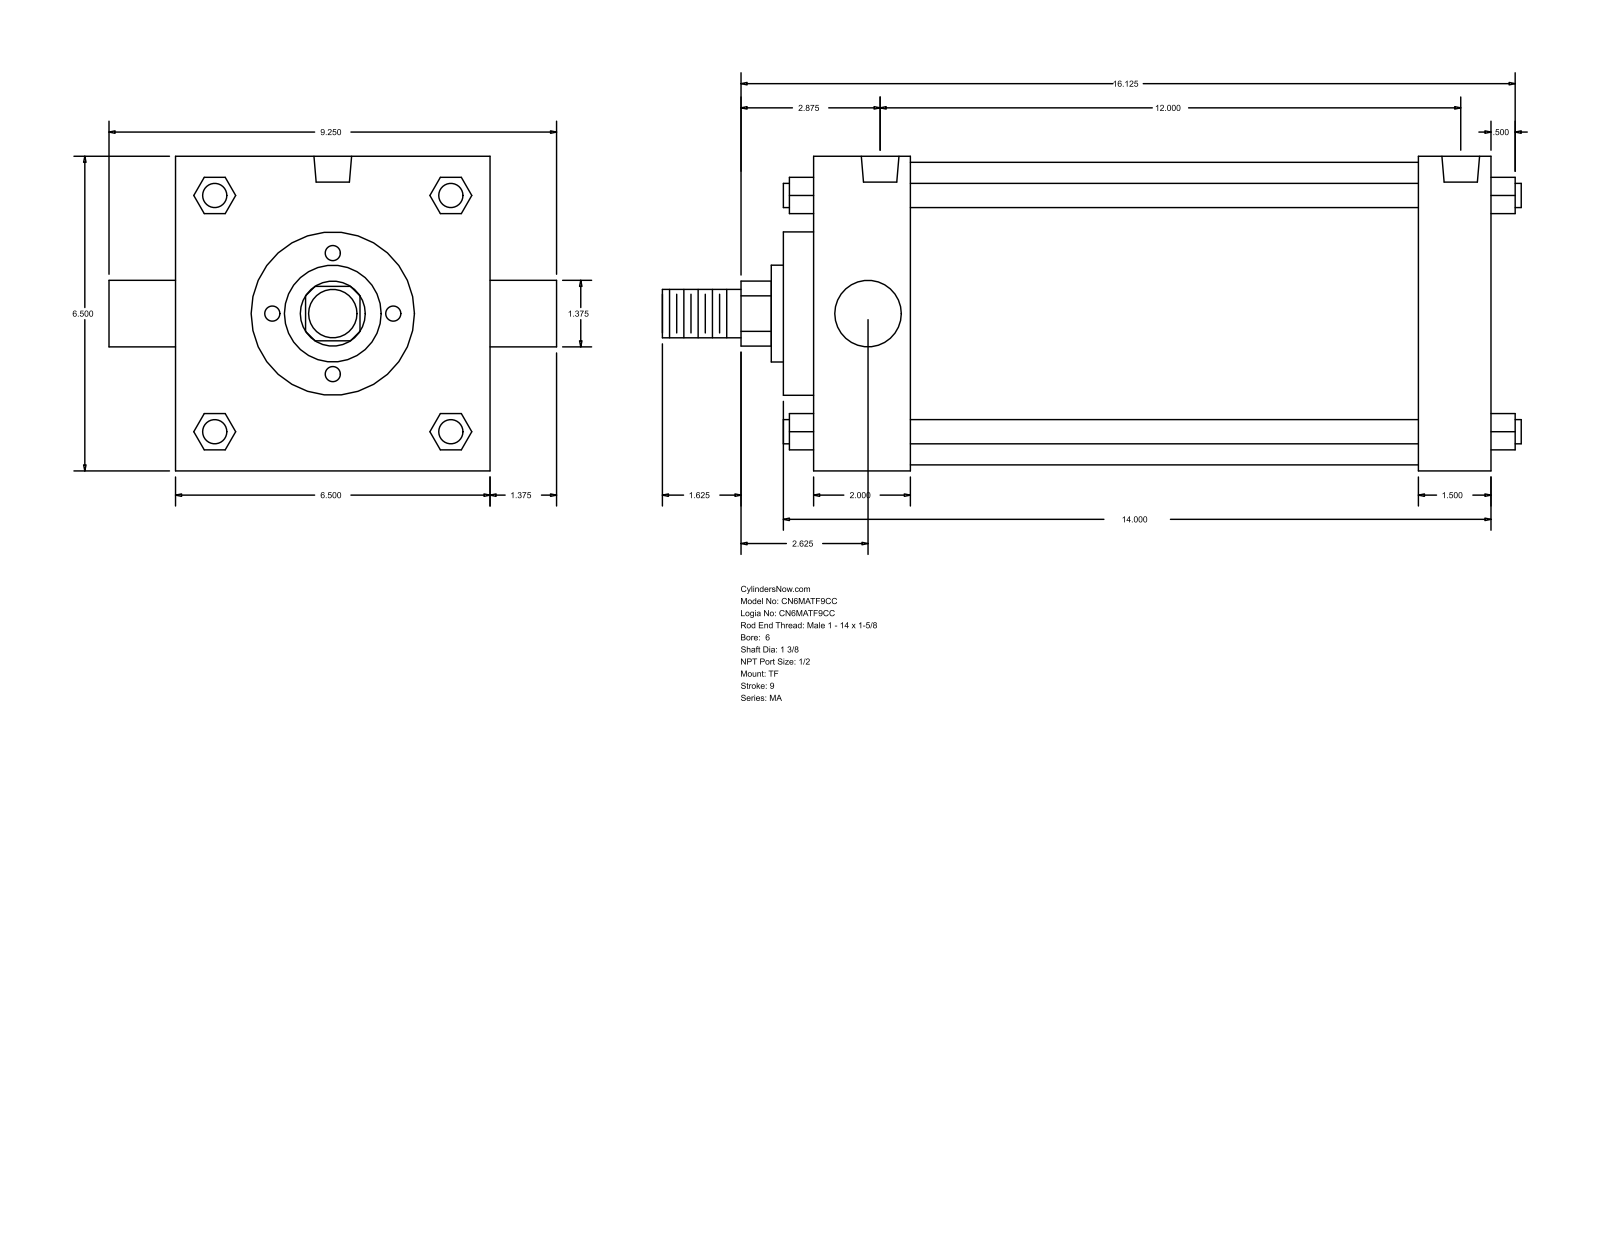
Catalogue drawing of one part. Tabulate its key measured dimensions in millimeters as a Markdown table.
| quantity | value |
| --- | --- |
| part name | MA_TF__0600_1.375 |
| STEP written by | GSSL Pune (CONFIG_CONTROL_DESIGN) |
| units | millimeters |
| bodies | 0 solids, 122 faces (93 planar, 29 cylindrical, 0 other) |
| overall size | 450.85 × 234.95 × 165.1 |
| round holes (diameter × count) | 17.46 × 3, 19.77 × 2 |
| round bosses / shafts (diameter × count) | 12.7 × 4, 34.92 × 2, 158.75 × 1, 85.72 × 1, 50.8 × 1, 25.4 × 1 |
| partial cylindrical surfaces (radius × count) | 17.06 × 1 |
| main face-to-face distances | 165.1, 358.78, 50.8, 320.67, 307.98, 269.87, 38.11, 66.67, 15.87, 336.54 |
| hole center spacings | 3.18, 304.79, 307.97 |
